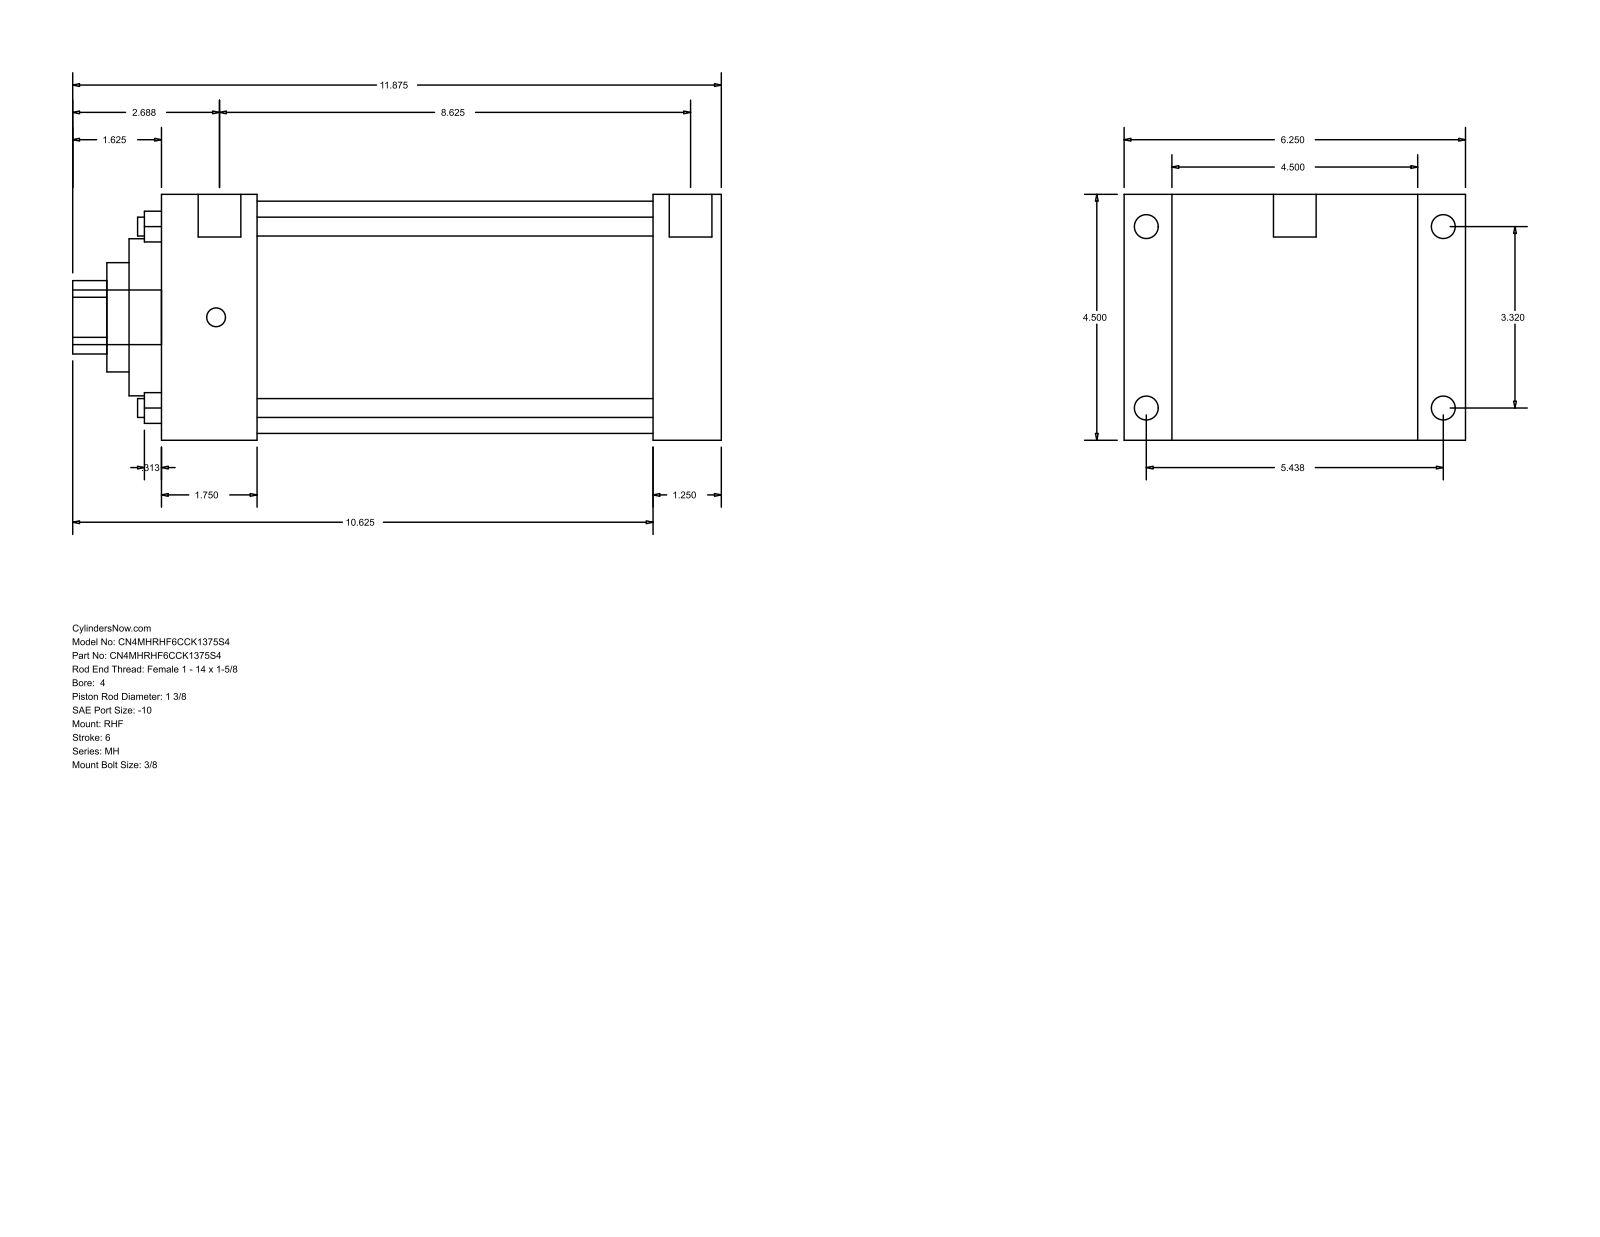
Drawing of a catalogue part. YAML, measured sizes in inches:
part_name: "MH_RHF__0400_1.375"
step_written_by: "GSSL Pune (CONFIG_CONTROL_DESIGN)"
units: inches
bodies: {solids: 0, faces: 90, planar: 61, cylindrical: 29, other: 0}
overall_size: [11.875, 6.25, 4.5]
round_holes:
  - {diameter: 0.345, count: 4}
  - {diameter: 1.375, count: 1}
  - {diameter: 2, count: 1}
  - {diameter: 2.875, count: 1}
  - {diameter: 4.25, count: 1}
round_bosses_or_shafts:
  - {diameter: 0.438, count: 4}
  - {diameter: 0.344, count: 4}
  - {diameter: 0.781, count: 2}
  - {diameter: 1, count: 1}
partial_cylinders:
  - {radius: 0.672, count: 1}
face_to_face_distances: [4.5, 10.25, 9, 1.25, 0.875, 5.375, 1.75, 7.25, 8.5, 6.25]
hole_center_spacings: [2.347, 3.32, 4.695]
